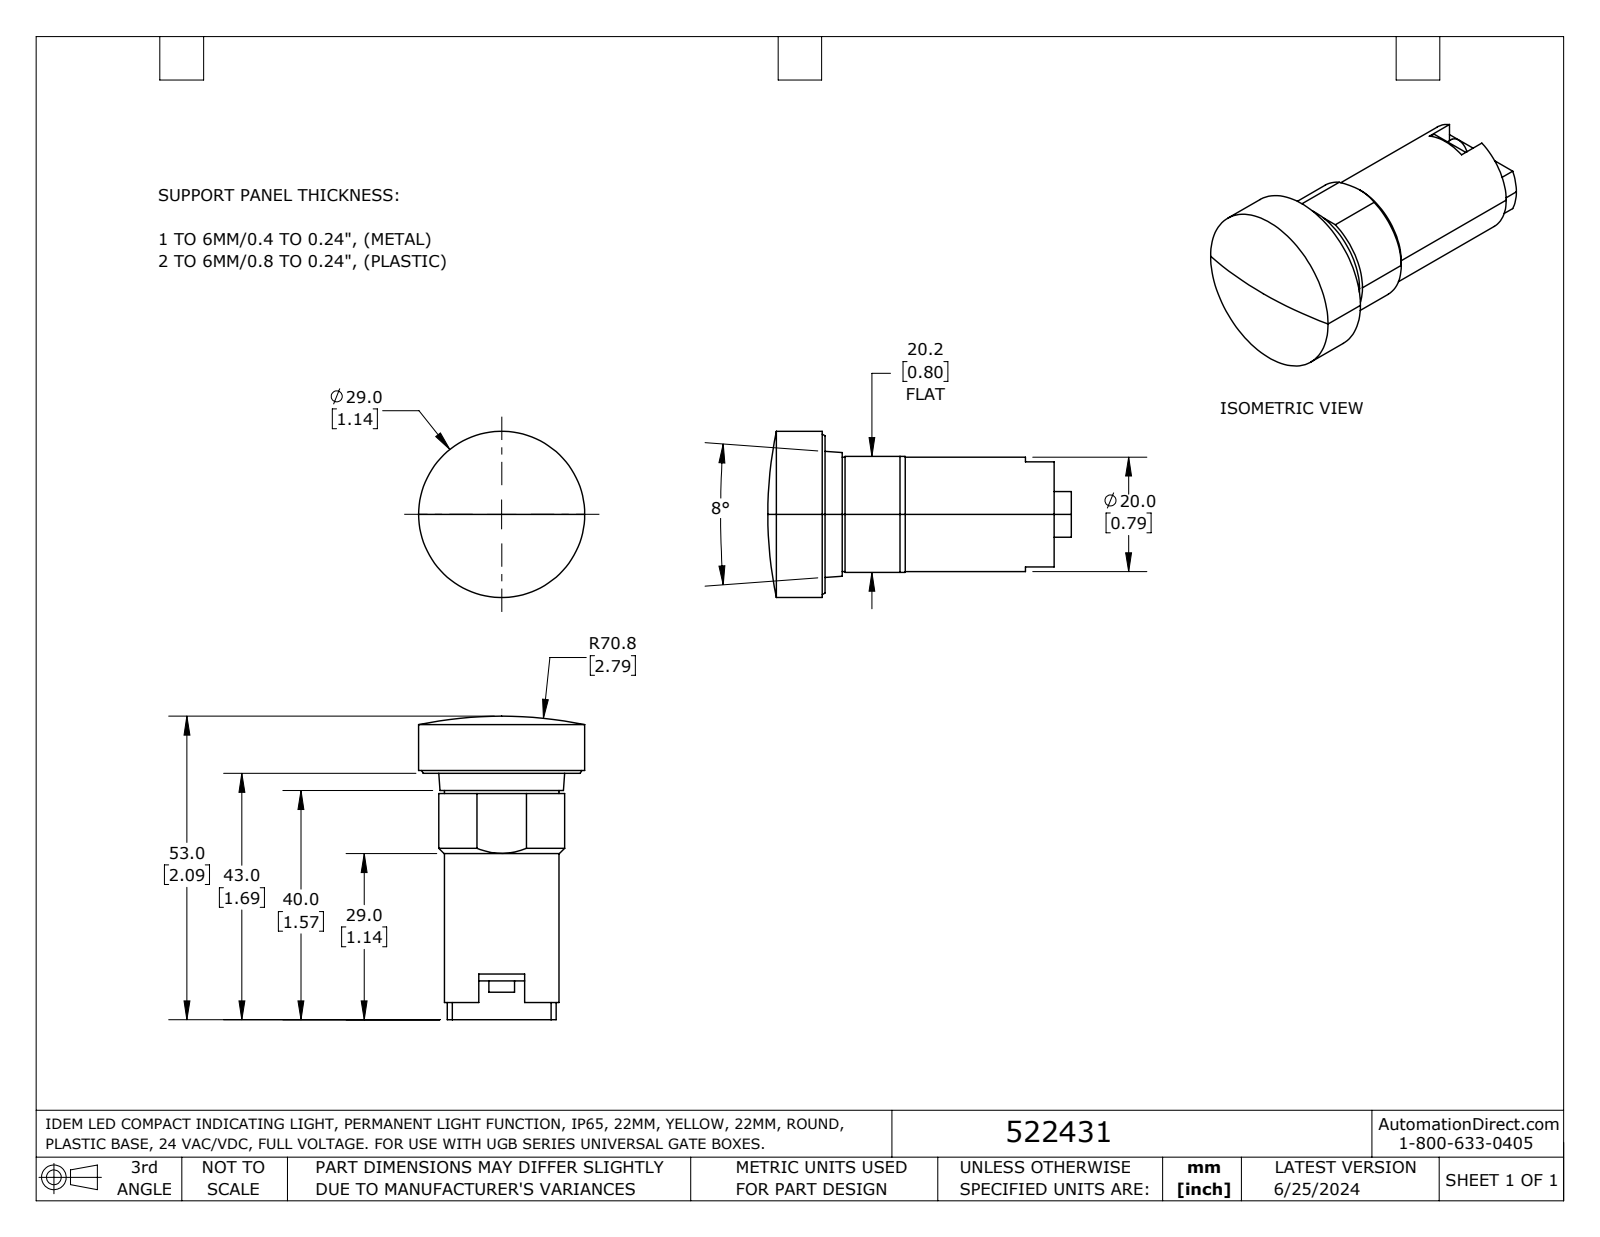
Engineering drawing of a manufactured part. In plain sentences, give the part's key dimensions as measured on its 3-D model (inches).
The part is named "522431". Its 3-D file was written by "SolidWorks 2023 (AUTOMOTIVE_DESIGN)". It is 1 solid with 50 faces: 24 planar, 18 cylindrical and 8 other. Overall it measures 2.087 by 1.142 by 1.142 inches. Its volume is 1.192 cubic inches and its surface area 7.789 square inches. Round bosses or shafts: 2 of diameter 0.177, 1 of diameter 1.142, 1 of diameter 0.787. Partial cylindrical surfaces (rounded edges, fillets, slot ends): 1 of radius 0.374, 1 of radius 0.433. The main face-to-face distances are 0.241, 0.556, 1.693, 0.315, 0.118, 1.575, 0.138, 0.02, 0.797, 1.437.
